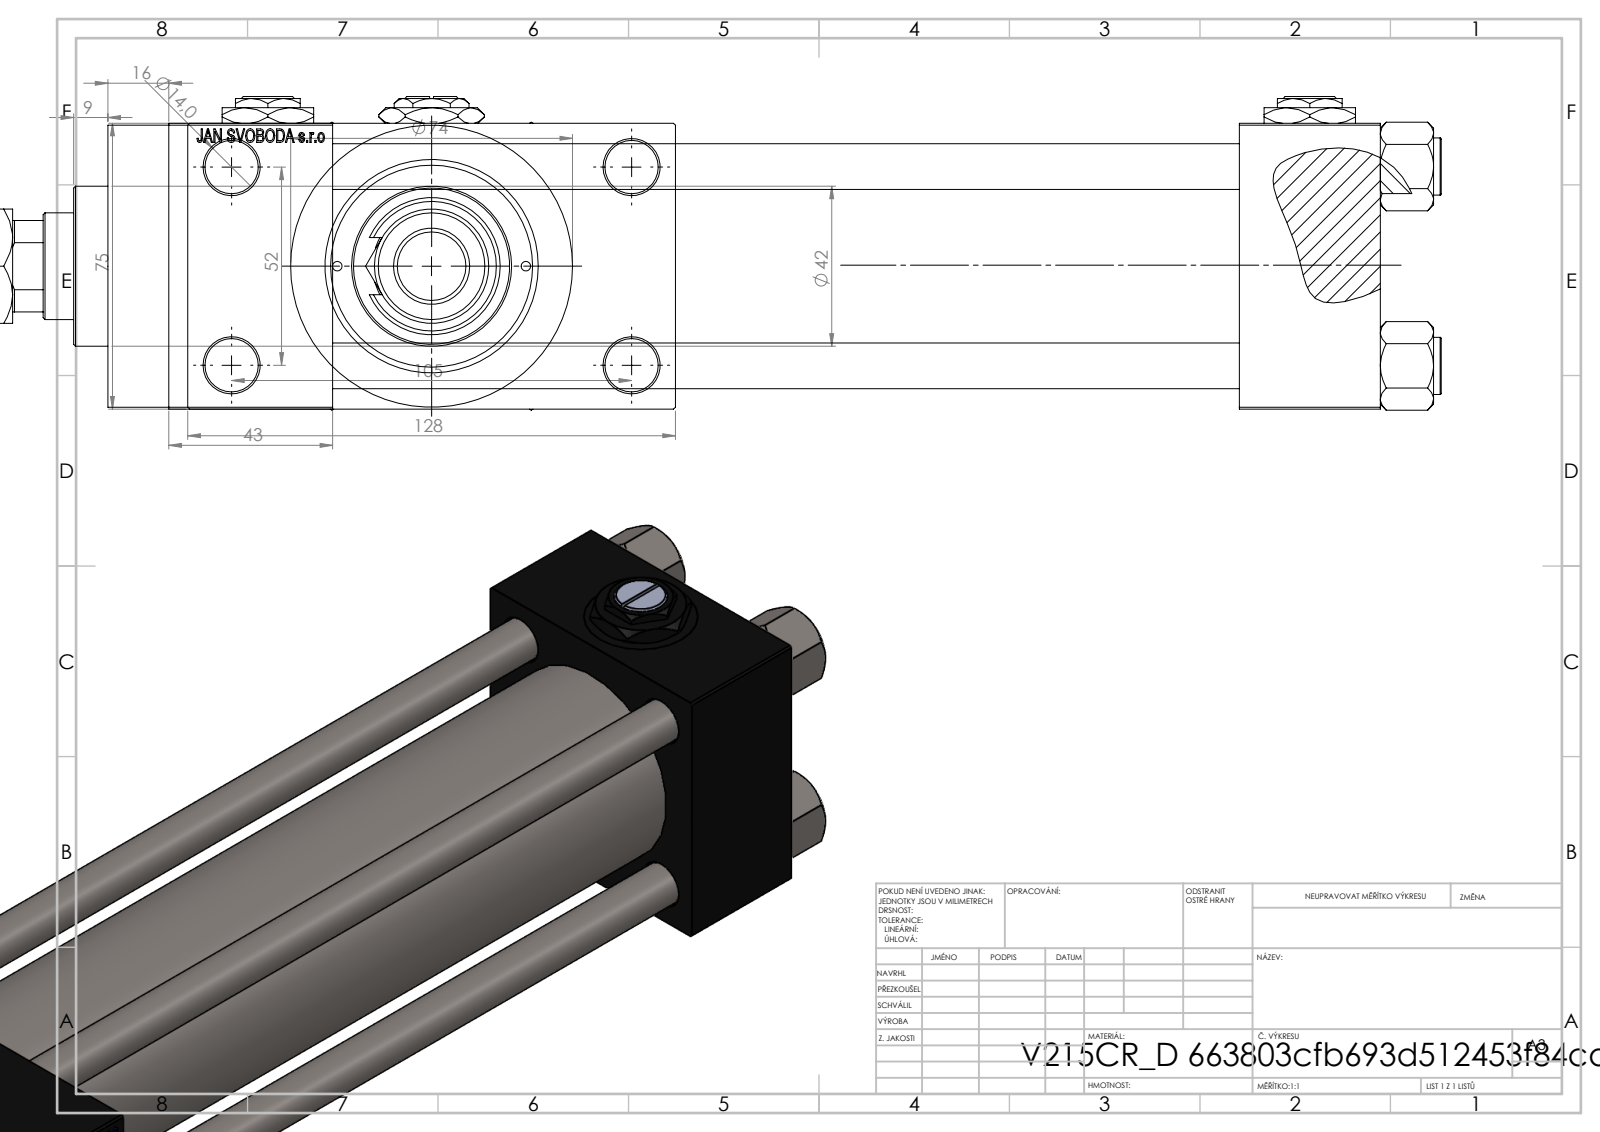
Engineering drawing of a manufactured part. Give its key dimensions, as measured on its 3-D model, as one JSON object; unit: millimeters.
{"part_name": "FEMALE_PART_FOR_DFA; Zatka_pro_OIL_PORT; V215CR_VCP_D; V215CR_D_TYCINKA (+4 more)", "step_written_by": "SolidWorks 2019 (CONFIG_CONTROL_DESIGN)", "units": "millimeters", "bodies": {"solids": 15, "faces": 1297, "planar": 575, "cylindrical": 116, "other": 606}, "overall_size": [459, 128, 82.27], "volume_mm3": 1133000, "surface_area_mm2": 290939, "round_holes": [[12, 4], [14, 4], [20.96, 4], [30, 4], [7, 3], [2.5, 2], [18.5, 1], [28, 1], [31, 1], [41, 1], [50, 1], [53, 1]], "round_bosses_or_shafts": [[15, 4], [74, 1], [56, 1], [42, 1], [36, 1], [30, 1], [22, 1], [20, 1]], "partial_cylinders_radius": [[7.5, 1], [12, 1], [13.5, 1]], "face_to_face_distances": [75, 238, 37, 275, 26.5, 43, 318, 281, 101.5, 16], "hole_center_spacings": [26.19, 26.35, 36.98, 38.03, 52.3, 57.22, 58.43, 58.59]}
